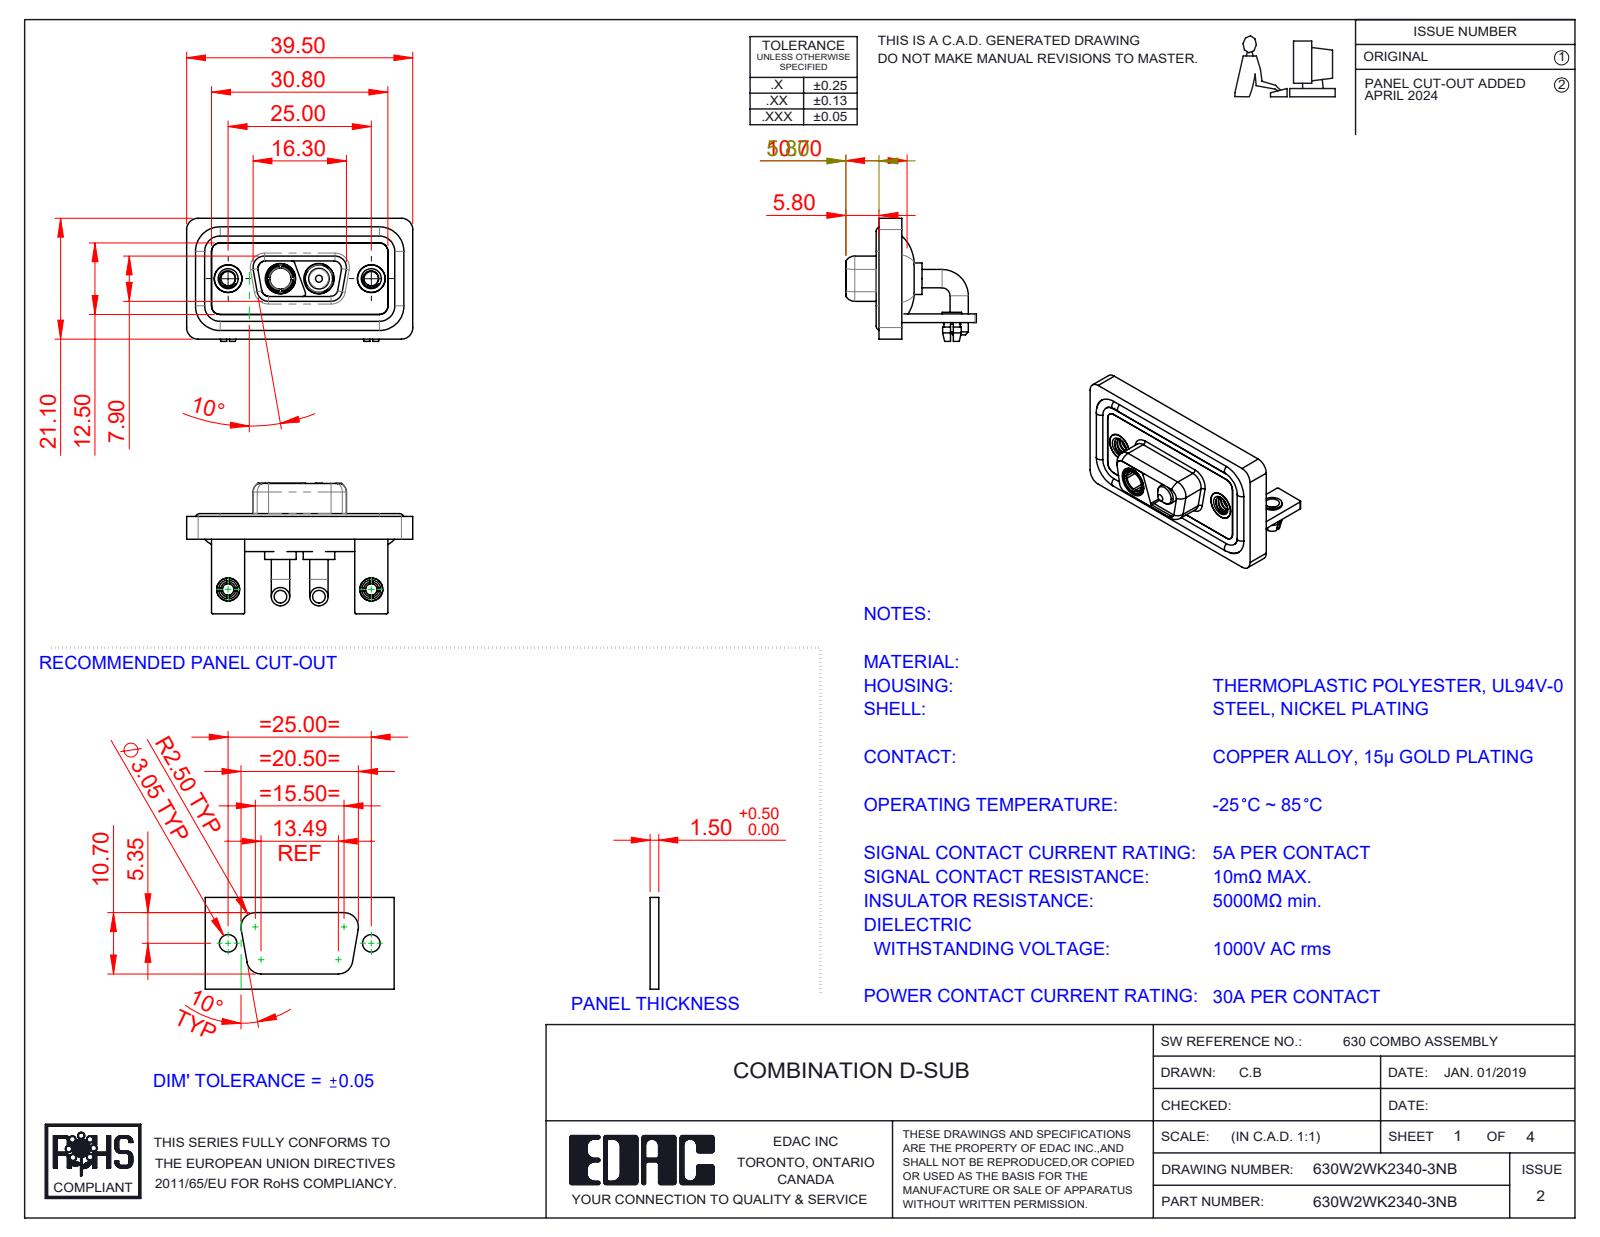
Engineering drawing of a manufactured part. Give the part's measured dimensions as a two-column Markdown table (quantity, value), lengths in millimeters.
| quantity | value |
| --- | --- |
| part name | 630Combo Shell Front_09 Contacts; 630Combo Waterproof Housing_09 Contacts; 630Combo Board Lock_50 Contacts; 630Combo Stabilizer Bracket_50 Contacts (+6 more) |
| STEP written by | SolidWorks 2023 (CONFIG_CONTROL_DESIGN) |
| units | millimeters |
| bodies | 15 solids, 642 faces (212 planar, 289 cylindrical, 141 other) |
| overall size | 39.5 × 22.8 × 21.5 |
| volume | 5 158 mm³ |
| surface area | 8 480 mm² |
| round holes (diameter × count) | 2.5 × 4, 4.85 × 4, 2 × 2, 3.2 × 2, 4 × 2, 4.05 × 2, 5 × 2, 5.3 × 2, 3.7 × 1 |
| round bosses / shafts (diameter × count) | 3.2 × 4, 1.6 × 4, 5.5 × 2, 5.2 × 2, 4.95 × 2, 4.8 × 2, 4.75 × 2, 4 × 2 |
| partial cylindrical surfaces (radius × count) | 2 × 19, 1.5 × 18, 0.25 × 16, 1.35 × 8, 1.6 × 8, 0.5 × 7, 0.6 × 4, 0.65 × 4 |
| main face-to-face distances | 0.4, 2.9, 1.5, 1.1, 3.7, 1.8, 0.8, 2.5, 1.6, 3.1 |
| hole center spacings | 9.14, 15.86, 25, 6.72 |
